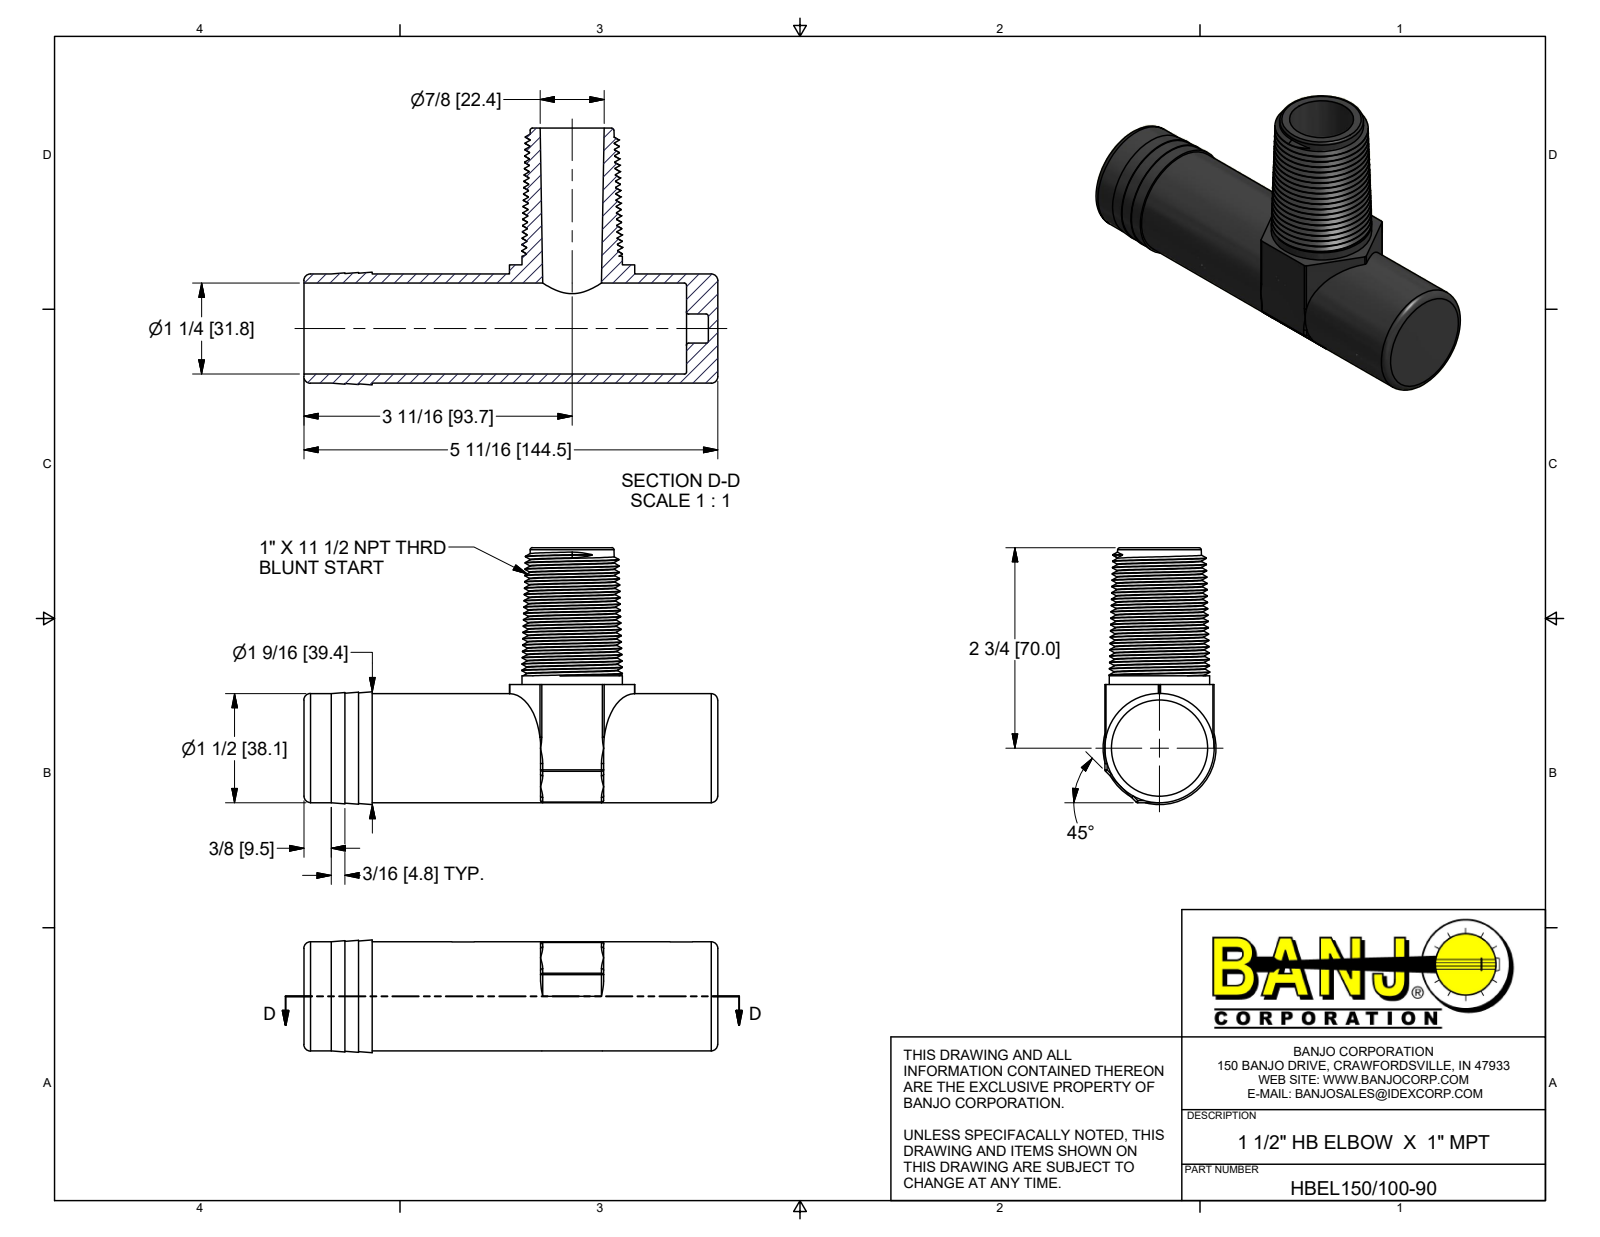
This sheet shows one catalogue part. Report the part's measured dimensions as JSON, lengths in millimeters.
{"part_name": "HBEL150-100-90", "step_written_by": "Autodesk Inventor 2017 (AUTOMOTIVE_DESIGN)", "units": "millimeters", "bodies": {"solids": 1, "faces": 97, "planar": 23, "cylindrical": 25, "other": 49}, "overall_size": [144.53, 89.66, 39.37], "volume_mm3": 86527, "surface_area_mm2": 45302, "round_holes": [[7.87, 1], [10.16, 1], [31.75, 1]], "round_bosses_or_shafts": [[38.1, 1], [35.05, 1]], "partial_cylinders_radius": [[0.76, 14], [8.94, 1], [19.02, 1]], "face_to_face_distances": [38.1, 10.92, 47.76, 41.27, 89.03, 133.6, 144.52, 44.32, 3.05, 44.71]}
